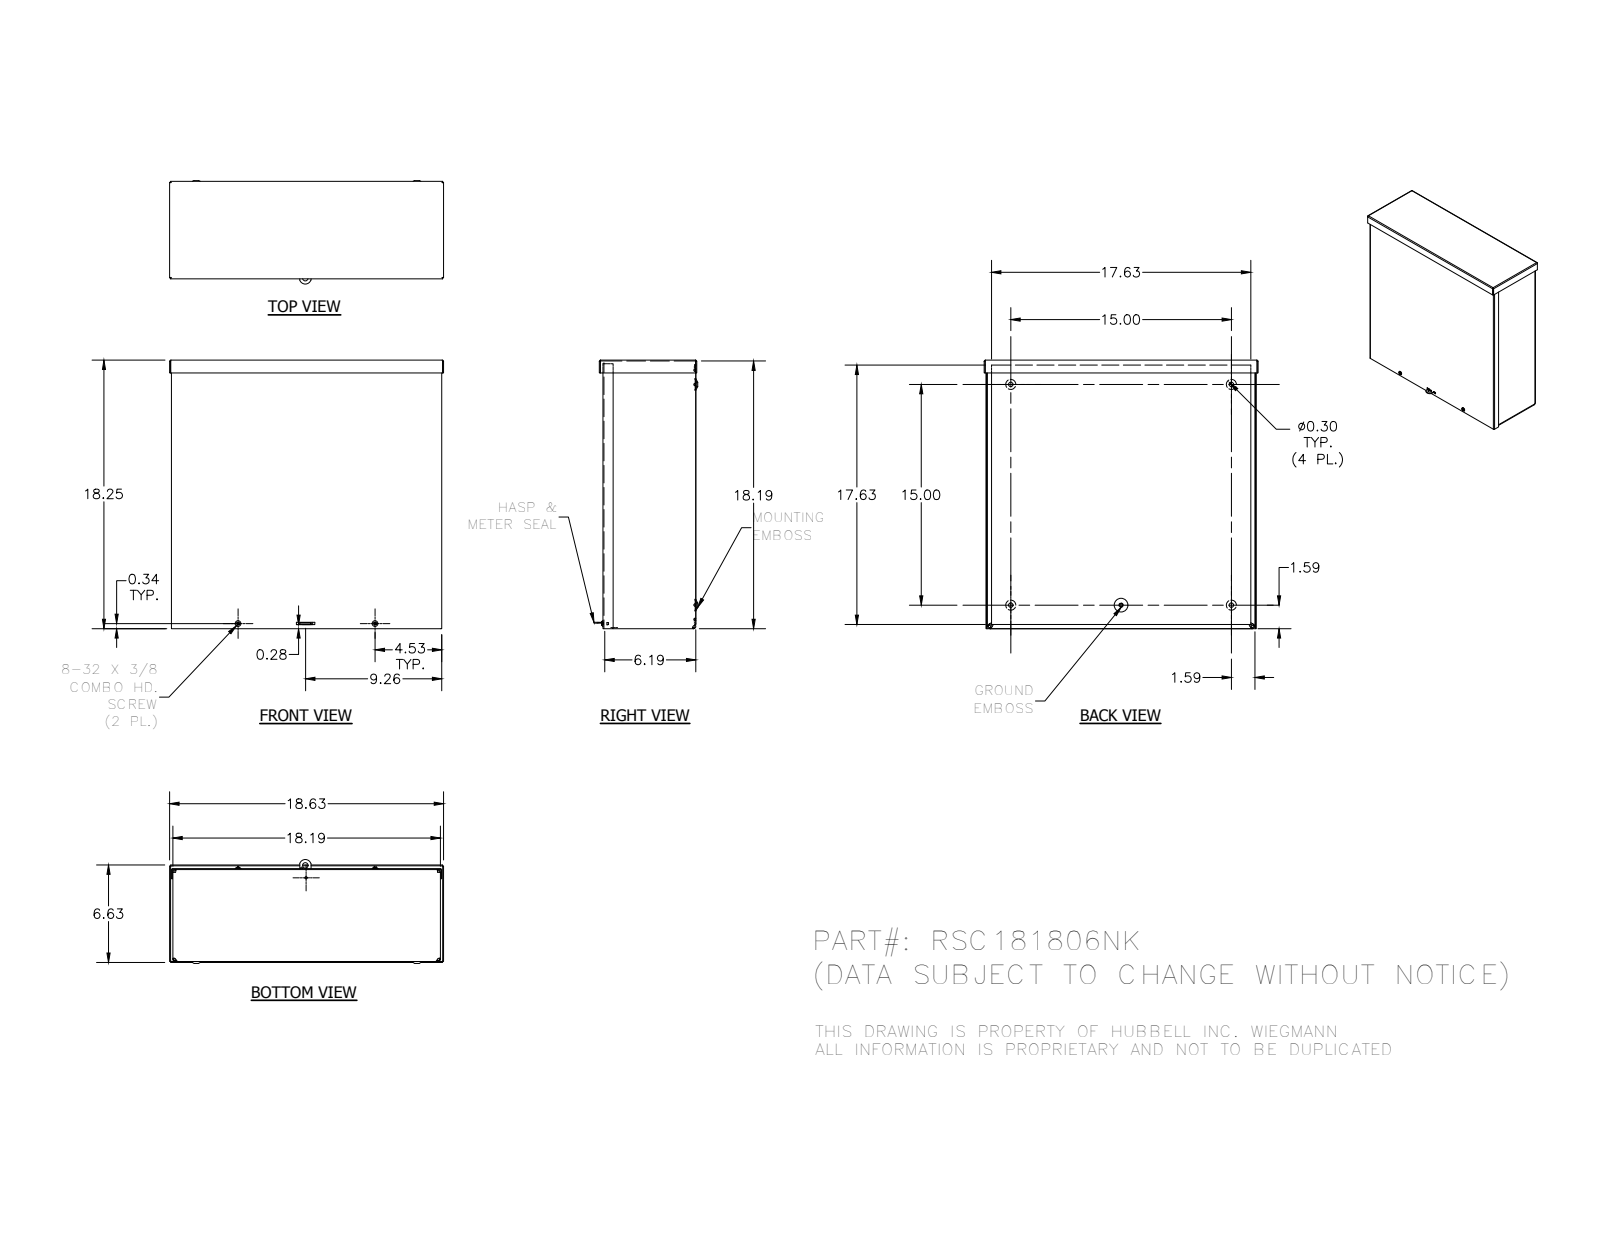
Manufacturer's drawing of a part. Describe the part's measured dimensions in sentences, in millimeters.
The part is named "RSC181806NK_WRAP; RSC1818NK_LID; RSC1806NK_CAP; 3183 (+3 more)". Its 3-D file was written by "Autodesk Inventor 2014 (AUTOMOTIVE_DESIGN)". It is 7 solids with 377 faces: 163 planar, 78 cylindrical and 136 other. Overall it measures 473.07 by 463.56 by 180.97 millimeters. Its volume is 1 402 000 cubic millimeters and its surface area 1 793 000 square millimeters. Round holes: 4 of diameter 7.62, 4 of diameter 7.95, 2 of diameter 3.76, 1 of diameter 3.17, 1 of diameter 3.45, 1 of diameter 3.96, 1 of diameter 4.19, 1 of diameter 9.52. Round bosses or shafts: 2 of diameter 9.75, 2 of diameter 4.17, 1 of diameter 5.8. Partial cylindrical surfaces (rounded edges, fillets, slot ends): 8 of radius 0.79, 8 of radius 2.37, 8 of radius 3.17, 8 of radius 4.75, 4 of radius 1.4, 4 of radius 1.57, 4 of radius 2.38, 4 of radius 2.97. The main face-to-face distances are 1.58, 460.39, 158.73, 157.15, 1.59, 160.32, 158.74, 1.57, 461.97, 3.15. The hole center spacings are 381, 190.5, 236.55, 419.05, 424.74, 425.96, 439.73, 499.32.
